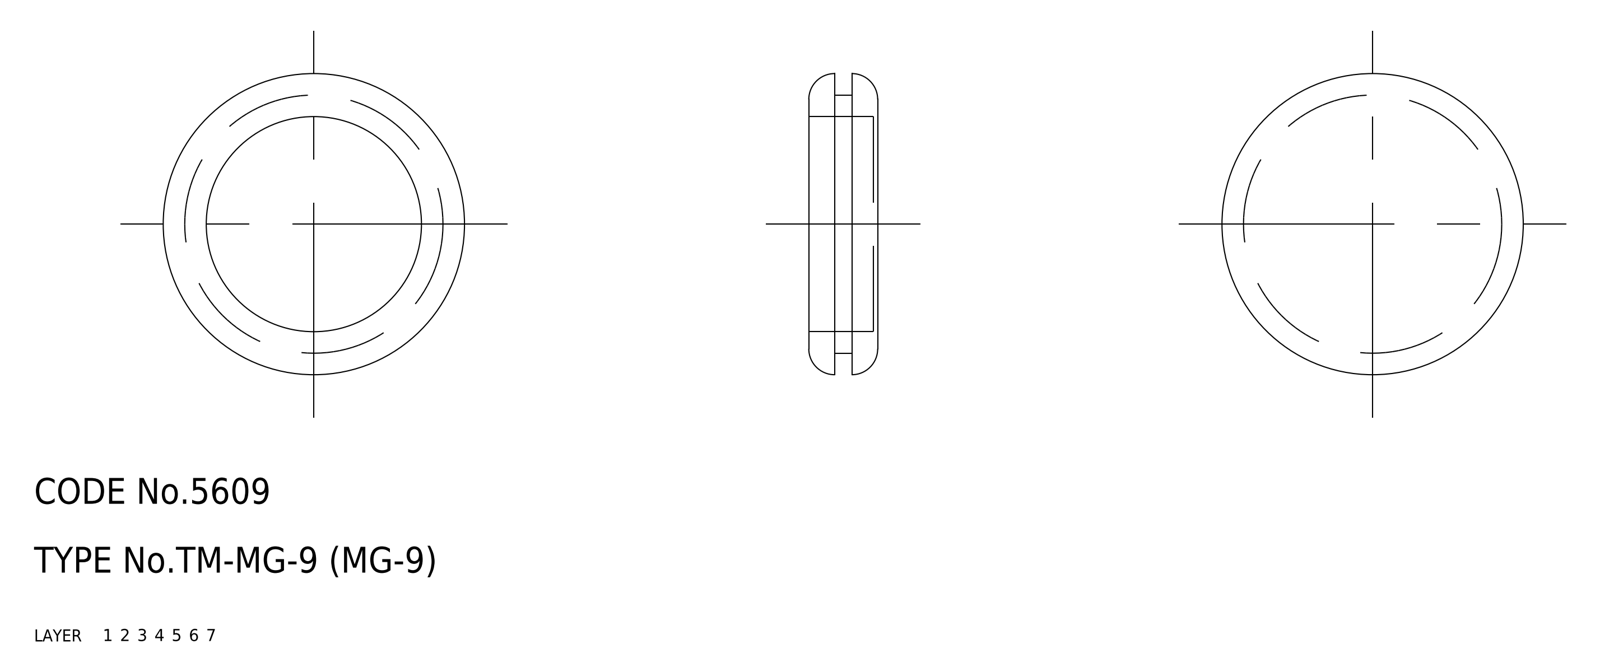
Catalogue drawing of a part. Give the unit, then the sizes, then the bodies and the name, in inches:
Units: inches
Overall size (bounding box): 1.378 × 1.378 × 0.315
Volume: 0.189 in³ · Surface area: 5.552 in²
Bodies: 1 solid, 13 faces (0 planar, 0 cylindrical, 13 other)
Part name (STEP PRODUCT): grommet
STEP written by: CADfix (AUTOMOTIVE_DESIGN)
